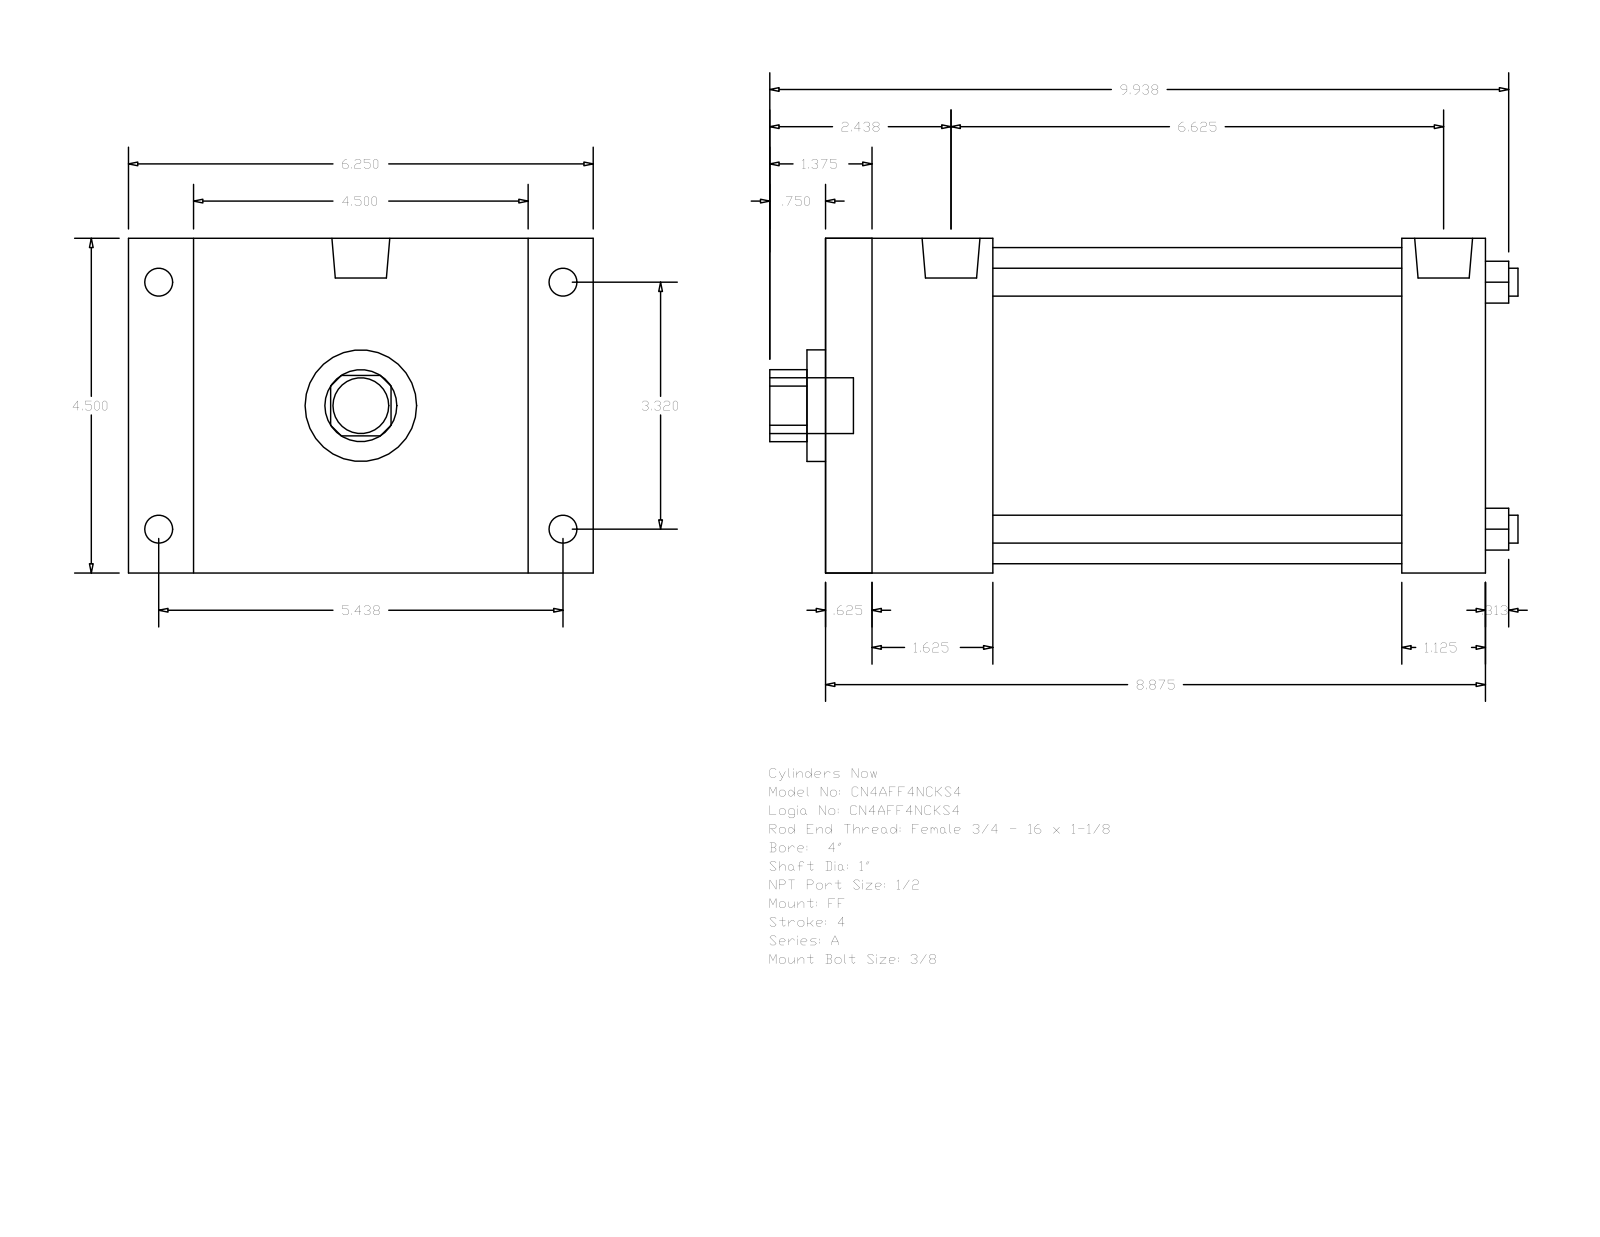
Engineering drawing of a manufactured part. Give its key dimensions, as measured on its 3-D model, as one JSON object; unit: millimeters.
{"part_name": "A_FF__0400_1", "step_written_by": "GSSL Pune (CONFIG_CONTROL_DESIGN)", "units": "millimeters", "bodies": {"solids": 0, "faces": 92, "planar": 64, "cylindrical": 28, "other": 0}, "overall_size": [255.59, 158.75, 114.3], "round_holes": [[9.53, 4], [25.4, 1], [38.1, 1], [107.95, 1]], "round_bosses_or_shafts": [[9.53, 4], [8.73, 4], [19.77, 2], [19.05, 1]], "partial_cylinders_radius": [[12.29, 1]], "face_to_face_distances": [114.3, 225.42, 15.87, 209.55, 28.57, 22.23, 136.53, 196.85, 180.98, 57.15], "hole_center_spacings": [59.62, 84.32, 119.25]}
